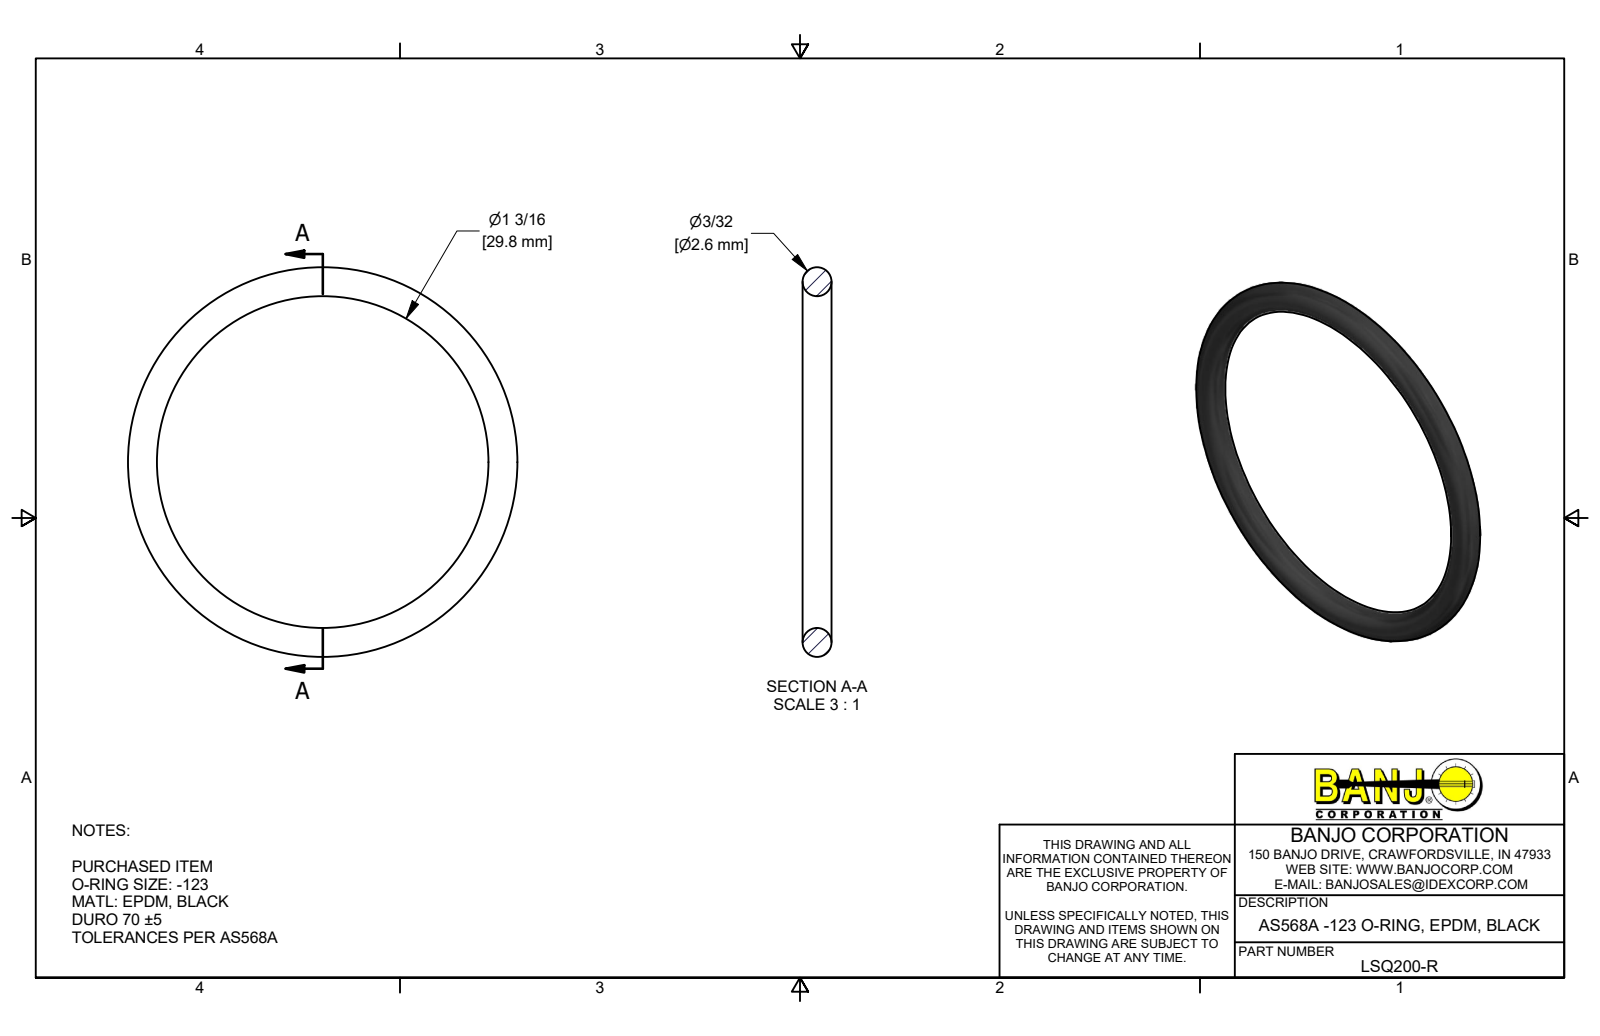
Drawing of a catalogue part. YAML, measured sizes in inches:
part_name: "LSQ200-R"
step_written_by: "Autodesk Inventor 2019 (AUTOMOTIVE_DESIGN)"
units: inches
bodies: {solids: 1, faces: 1, planar: 0, cylindrical: 0, other: 1}
overall_size: [1.38, 1.38, 0.103]
volume: 0.033
surface_area: 1.298
